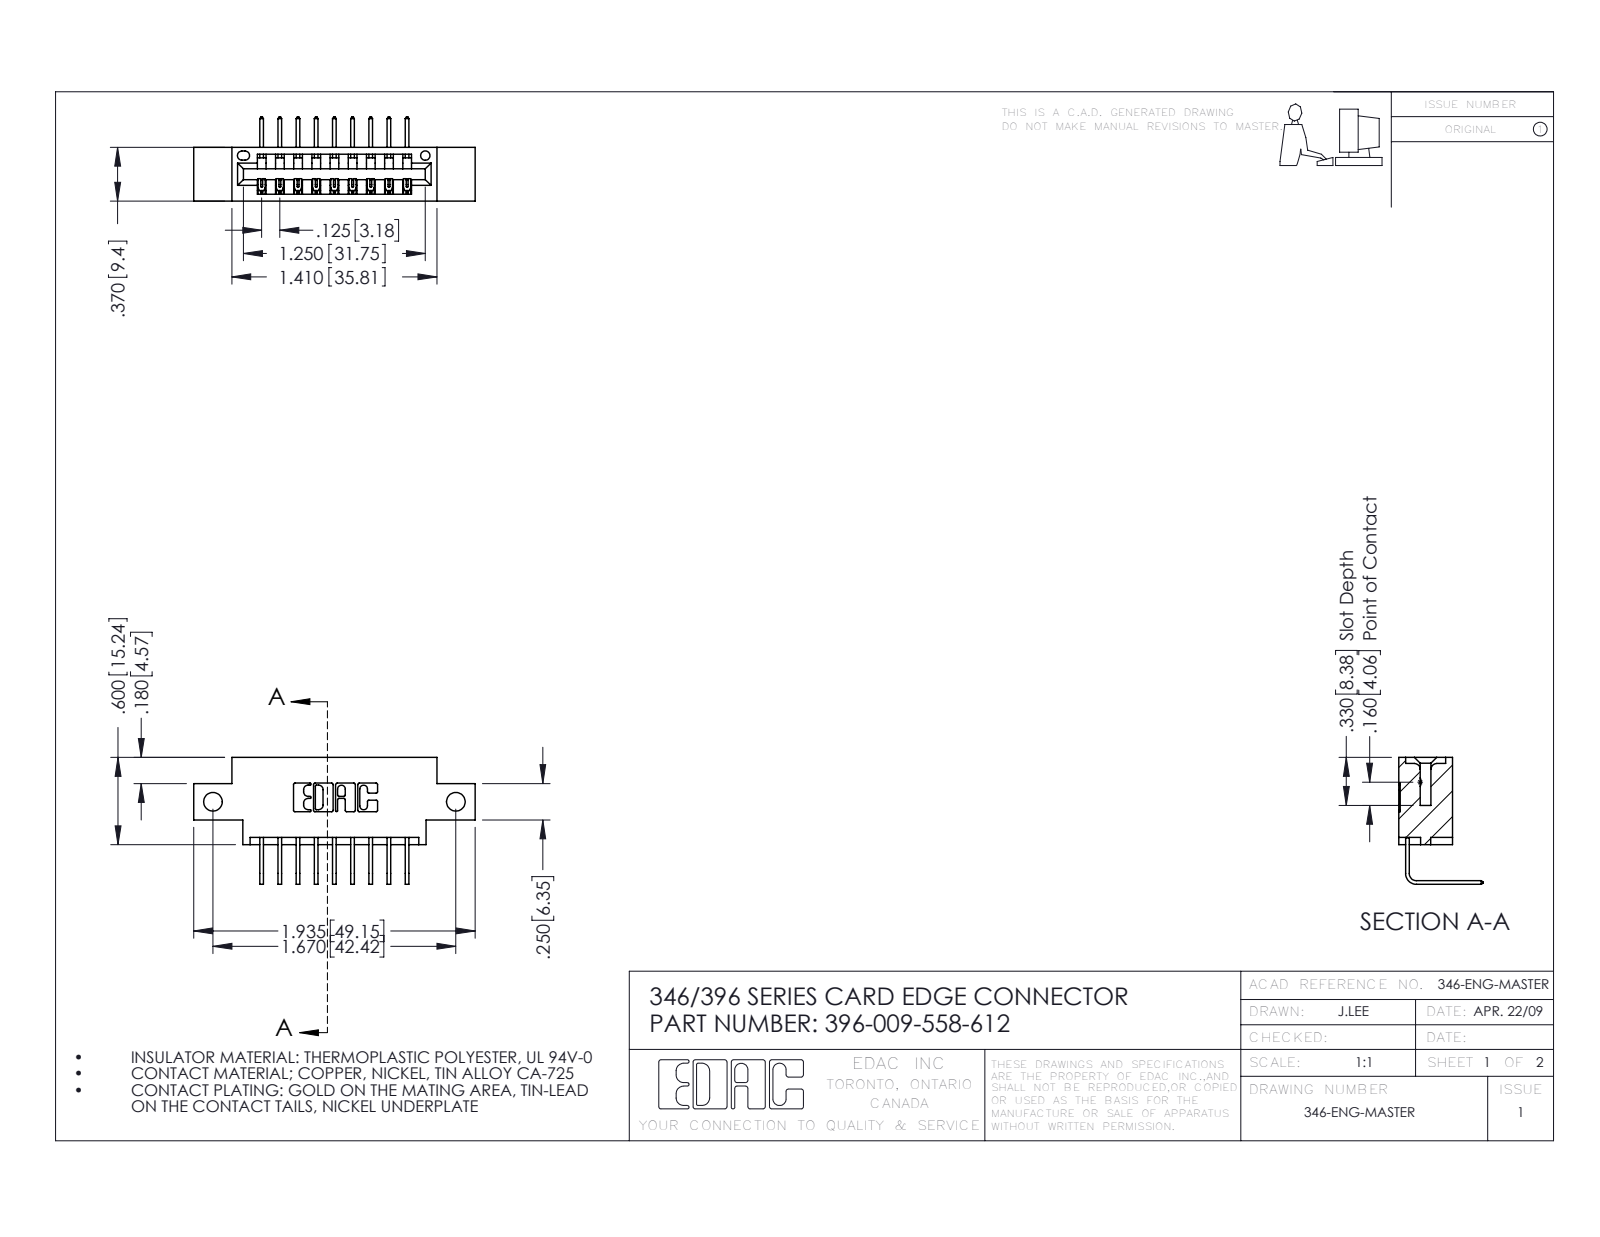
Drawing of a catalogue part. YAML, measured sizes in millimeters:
part_name: "396-009-558-612; 346 Part_0.170 Offset - Side Mount; 345-292-001_558 Tail - 2"
step_written_by: "SolidWorks 2016 (CONFIG_CONTROL_DESIGN)"
units: millimeters
bodies: {solids: 10, faces: 666, planar: 458, cylindrical: 208, other: 0}
overall_size: [49.1, 22.2, 14.7]
volume: 4260
surface_area: 5168
round_holes:
  - {diameter: 3.3, count: 2}
  - {diameter: 1.6, count: 1}
partial_cylinders:
  - {radius: 0.3, count: 22}
  - {radius: 0.2, count: 18}
  - {radius: 0.2, count: 6}
  - {radius: 0.8, count: 6}
  - {radius: 0.7, count: 3}
  - {radius: 0.8, count: 2}
  - {radius: 1, count: 2}
  - {radius: 0.4, count: 1}
face_to_face_distances: [6.4, 9.4, 8.2, 1.2, 7.6, 0.6, 3.8, 5.6, 2.5, 4.4]
hole_center_spacings: [42.4]
